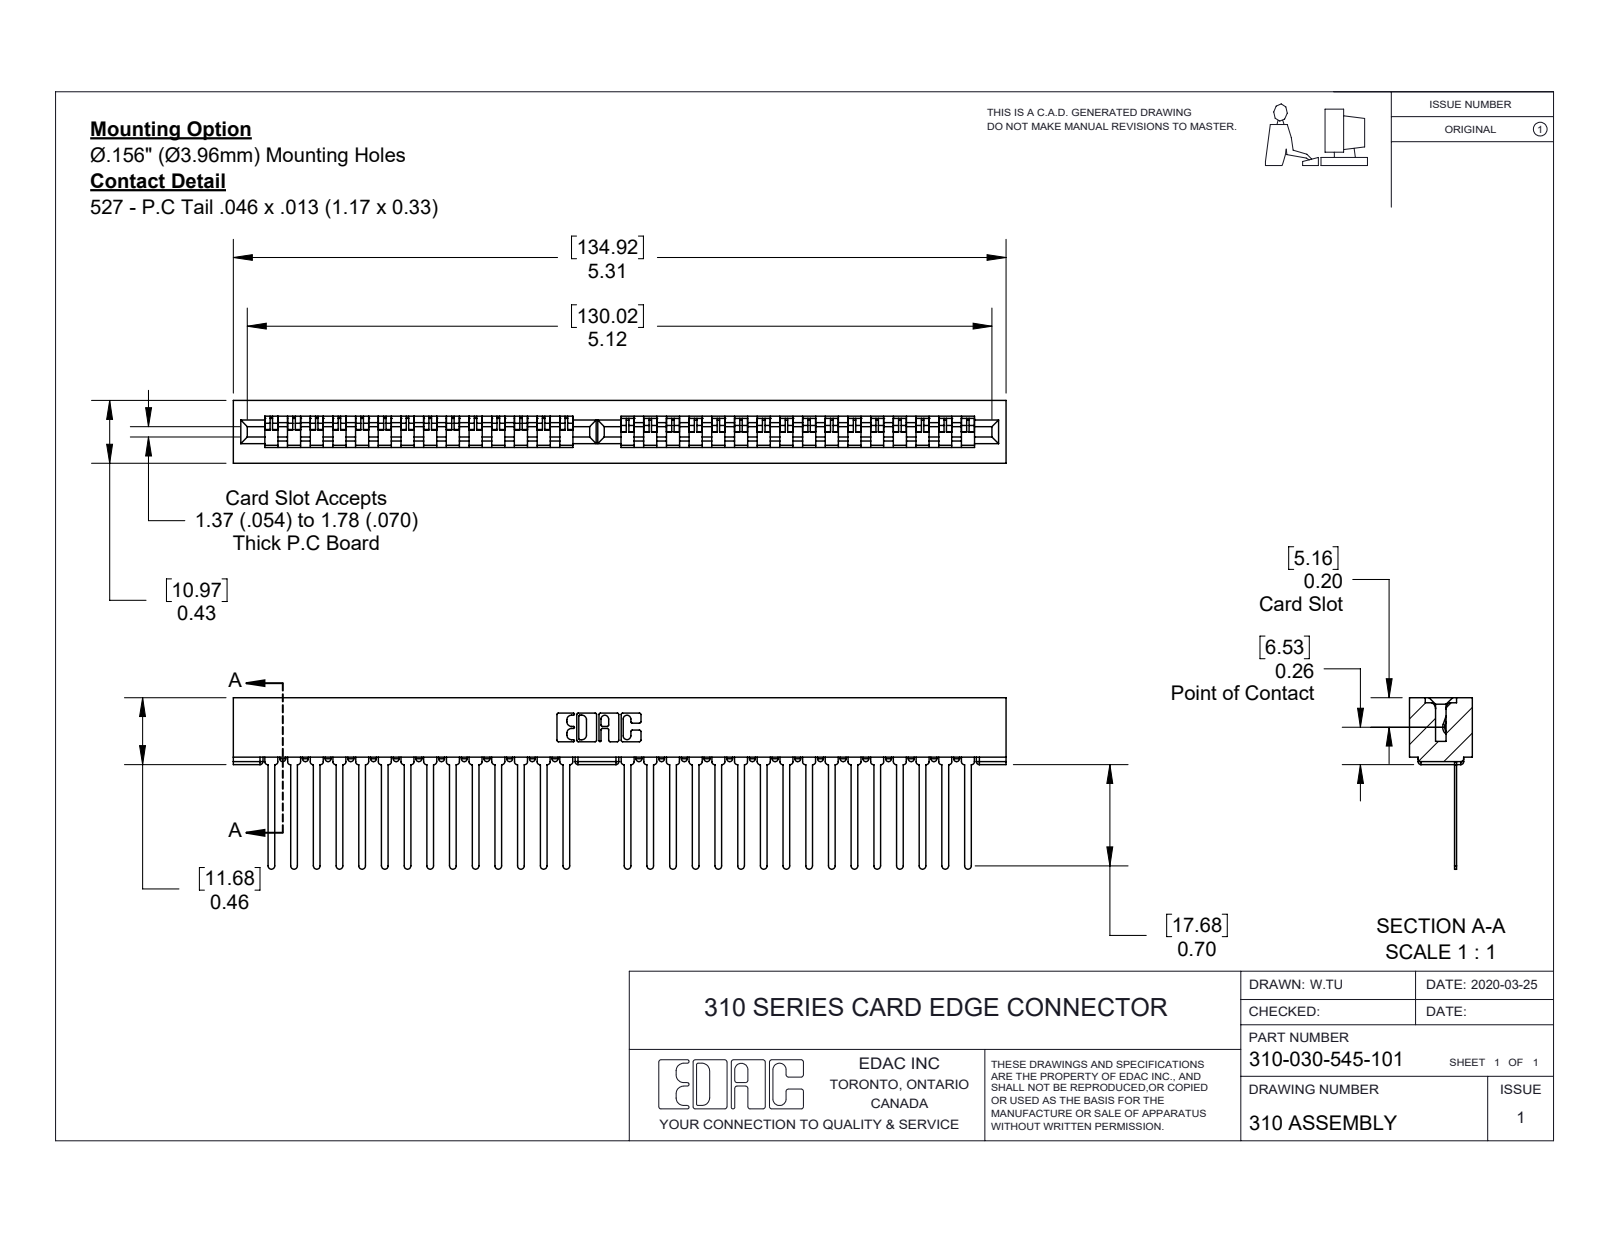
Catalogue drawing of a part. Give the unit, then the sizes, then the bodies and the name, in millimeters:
Units: millimetres
Overall size (bounding box): 134.93 × 29.95 × 10.97
Partial cylindrical surfaces — rounded edges, fillets, slot ends (radius × count): R0.51 ×158, R0.58 ×30, R0.25 ×22, R0.17 ×6, R0.8 ×6, R0.67 ×3, R0.3 ×2, R0.64 ×2
Main face-to-face distances: 2.76, 8.22, 0.38, 0.33, 10.98, 1.82, 3.14, 7.84, 5.08, 10.38
Volume: 11 791 mm³ · Surface area: 14 999 mm²
Bodies: 31 solids, 1838 faces (1190 planar, 584 cylindrical, 64 other)
Part name (STEP PRODUCT): 310 Part_No Mounting Lugs; 310-030-545-101; 307-290-001_545
STEP written by: SolidWorks 2016 (CONFIG_CONTROL_DESIGN)
